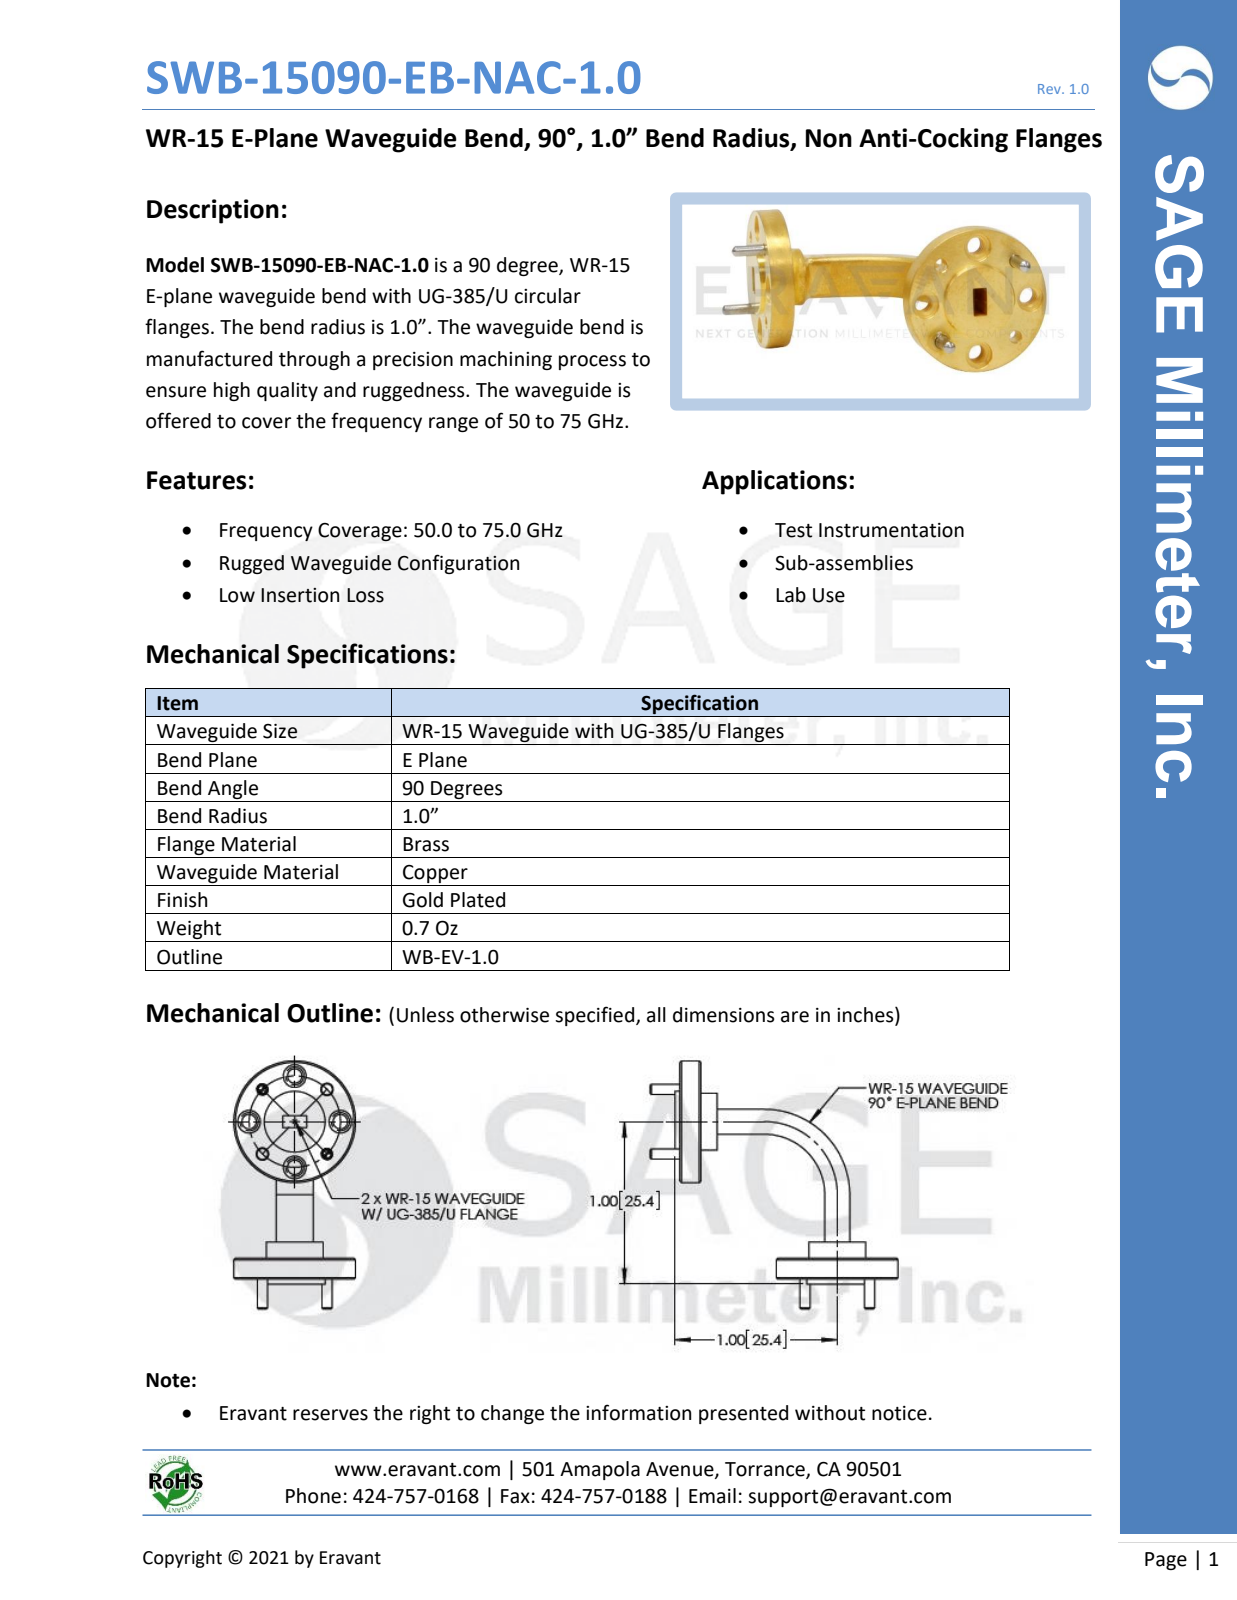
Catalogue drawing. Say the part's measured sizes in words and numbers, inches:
The part is named "SWB-15090-E1-1.0". Its 3-D file was written by "SolidWorks 2016 (AUTOMOTIVE_DESIGN)". It is 5 solids with 150 faces: 40 planar, 70 cylindrical and 40 other. Overall it measures 1.527 by 1.527 by 0.75 inches. Its volume is 0.178 cubic inches and its surface area 4.162 square inches. Round holes: 8 of diameter 0.089, 8 of diameter 0.14, 4 of diameter 0.061, 4 of diameter 0.067. Round bosses or shafts: 4 of diameter 0.063, 2 of diameter 0.75, 2 of diameter 0.375, 2 of diameter 0.35. Partial cylindrical surfaces (rounded edges, fillets, slot ends): 1 of radius 0.373, 1 of radius 0.527. The main face-to-face distances are 0.13, 0.03, 0.16, 0.228, 1.077, 1.047, 0.917, 0.923, 0.893, 0.763. The hole center spacings are 0.215, 0.398, 0.519, 0.562.
